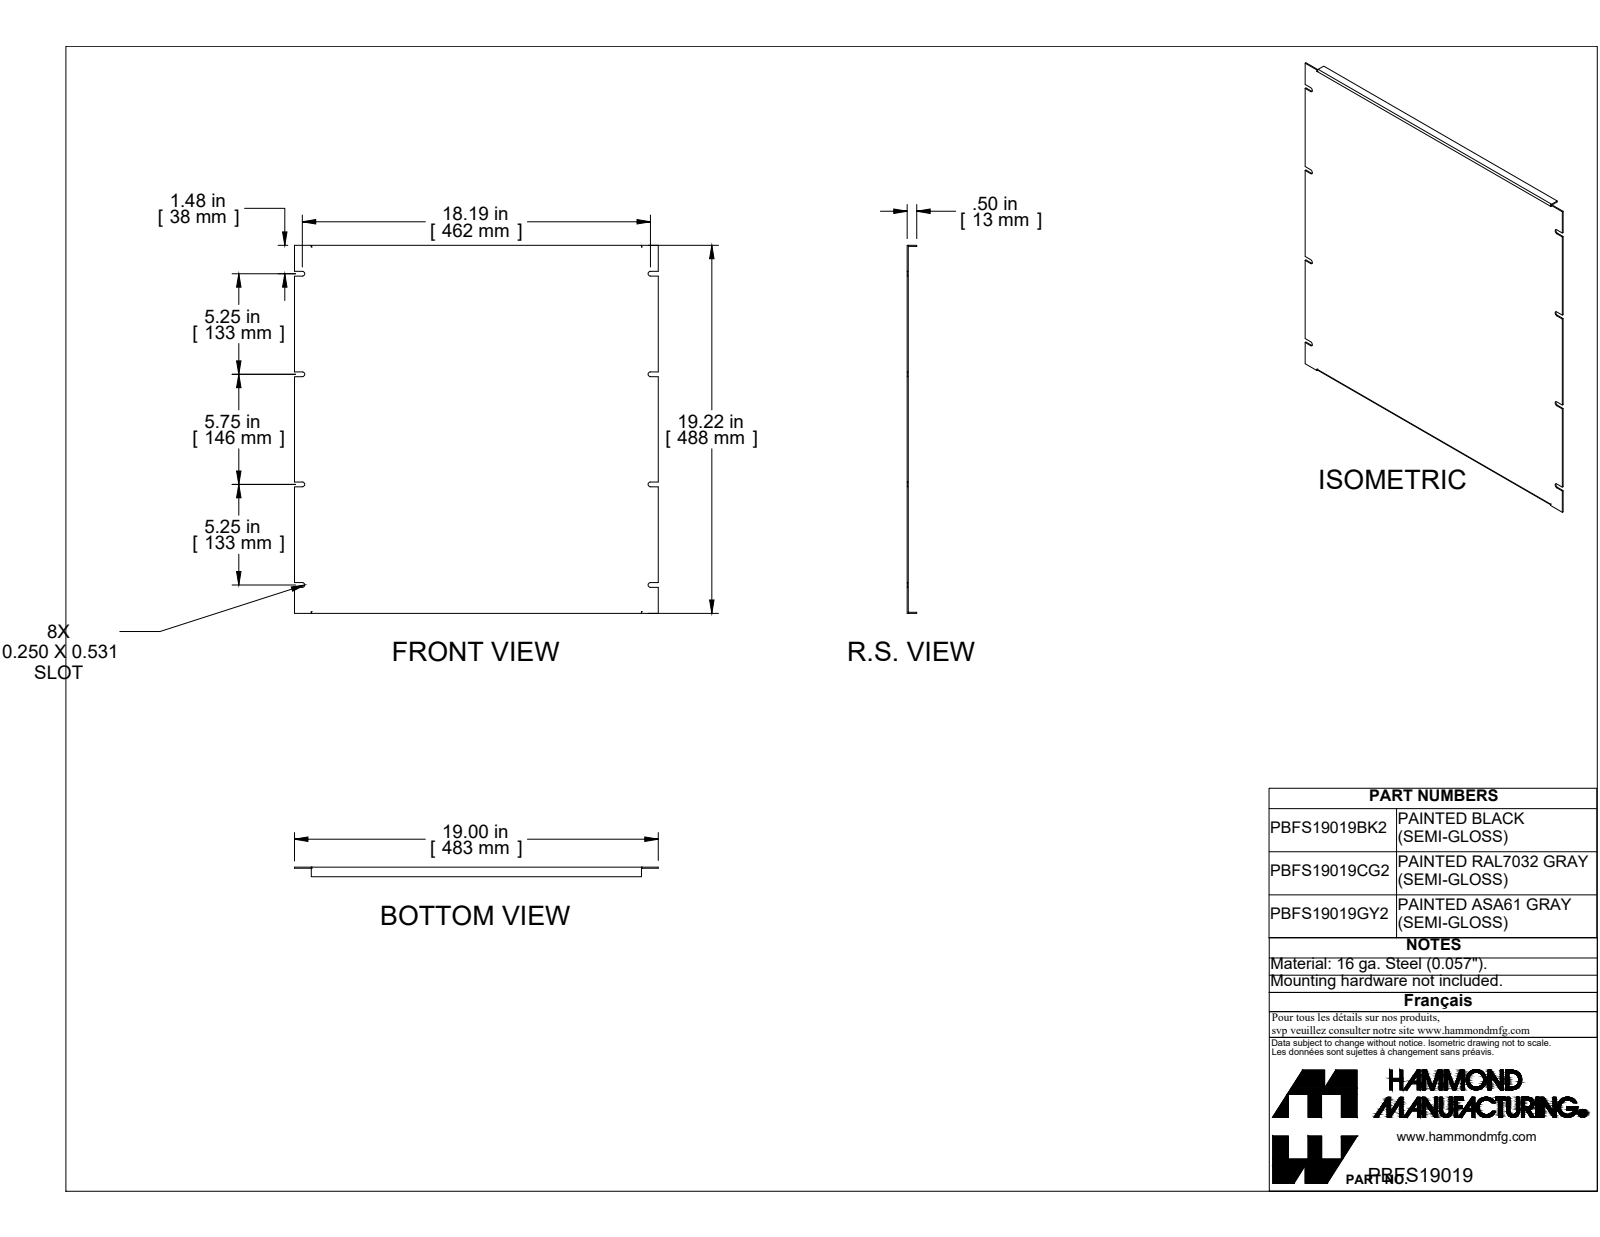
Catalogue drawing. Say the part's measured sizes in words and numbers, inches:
The part is named "PBFS19019". Its 3-D file was written by "SolidWorks 2019 (CONFIG_CONTROL_DESIGN)". It is 1 solid with 62 faces: 50 planar, 12 cylindrical and 0 other. Overall it measures 19.218 by 19 by 0.5 inches. Its volume is 21.58 cubic inches and its surface area 762.1 square inches. Partial cylindrical surfaces (rounded edges, fillets, slot ends): 8 of radius 0.125, 2 of radius 0.029, 2 of radius 0.086. The main face-to-face distances are 0.057, 19.161, 19.218, 19.104, 0.5, 0.443, 19, 0.25, 5.25, 11.
